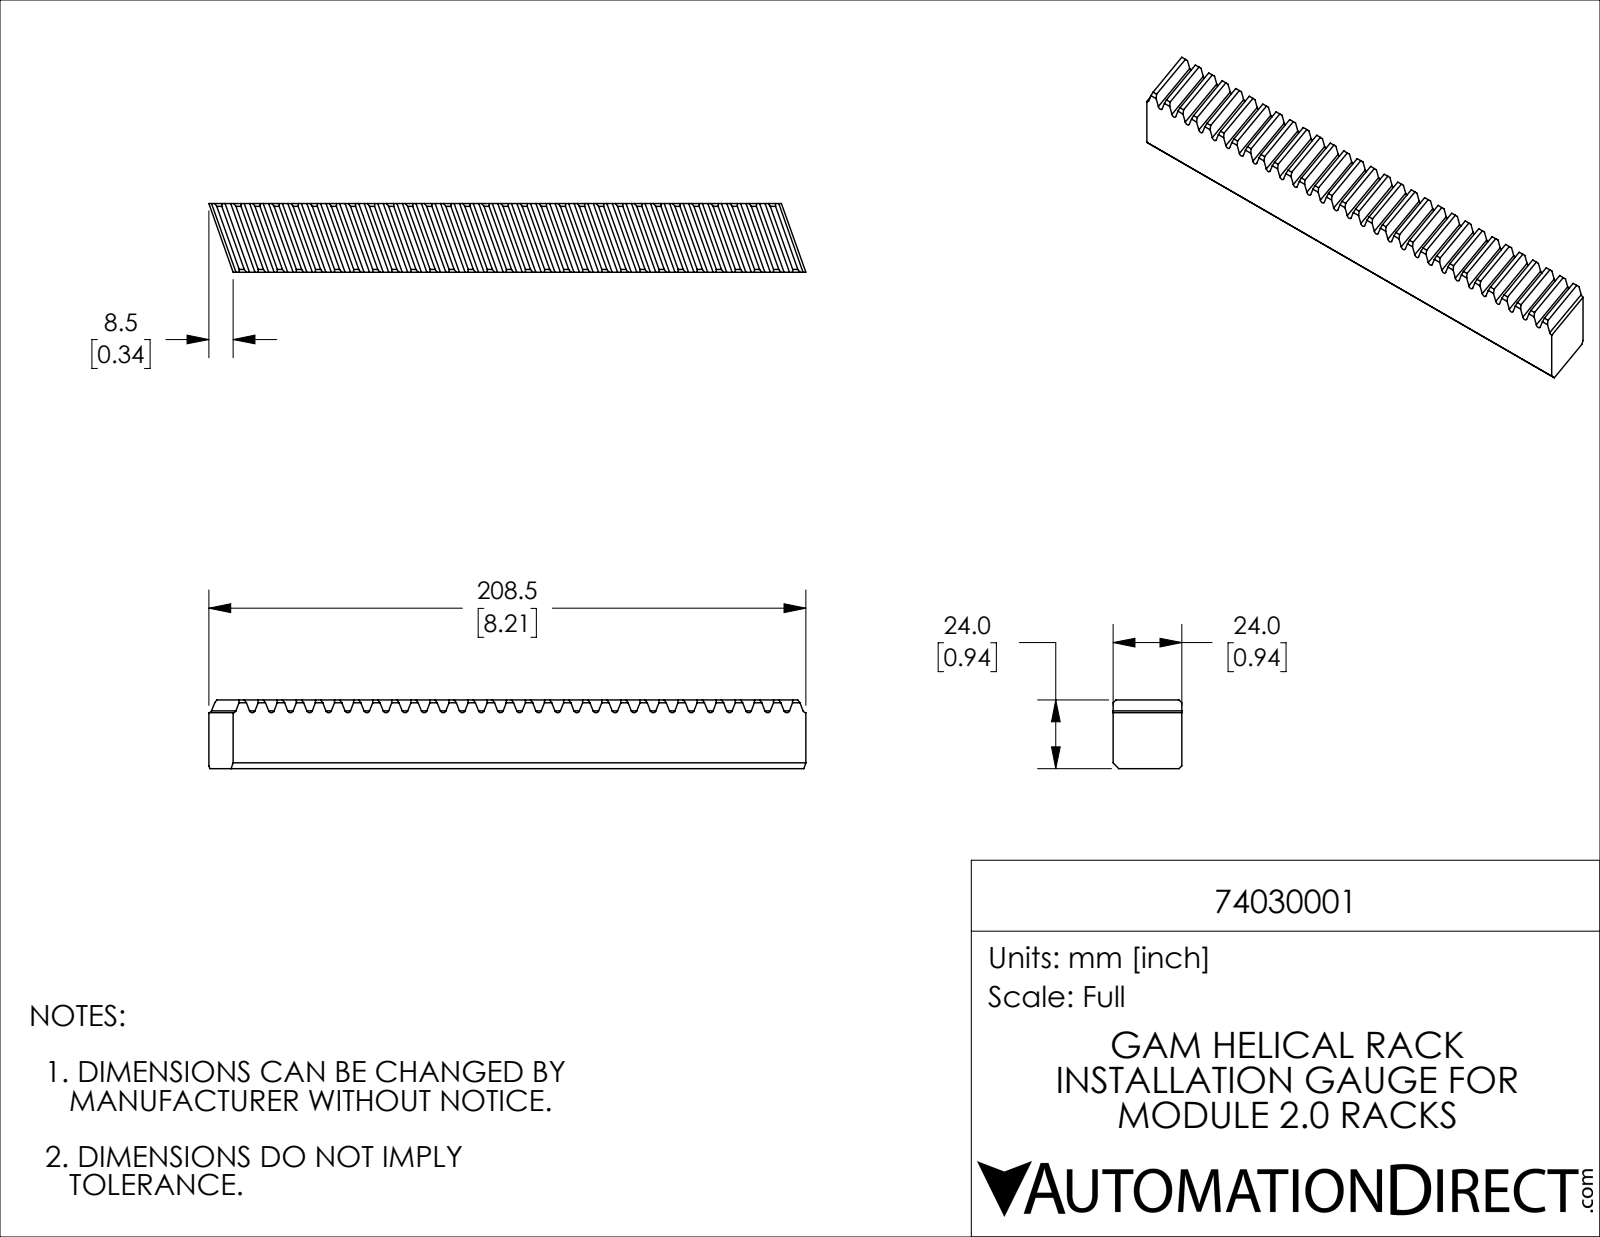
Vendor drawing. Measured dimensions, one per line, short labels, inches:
name: 74030001
written by: SolidWorks 2019 (CONFIG_CONTROL_DESIGN)
unit: in
bodies: 1 solid, 188 faces (157 planar, 0 cylindrical, 31 other)
size: 8.209 × 0.945 × 0.945
volume: 6.383 in³; area: 36.31 in²
face distances: 0.945, 0.698, 1.395, 2.093, 0.233, 2.791, 0.93, 1.163, 0.465, 1.628
